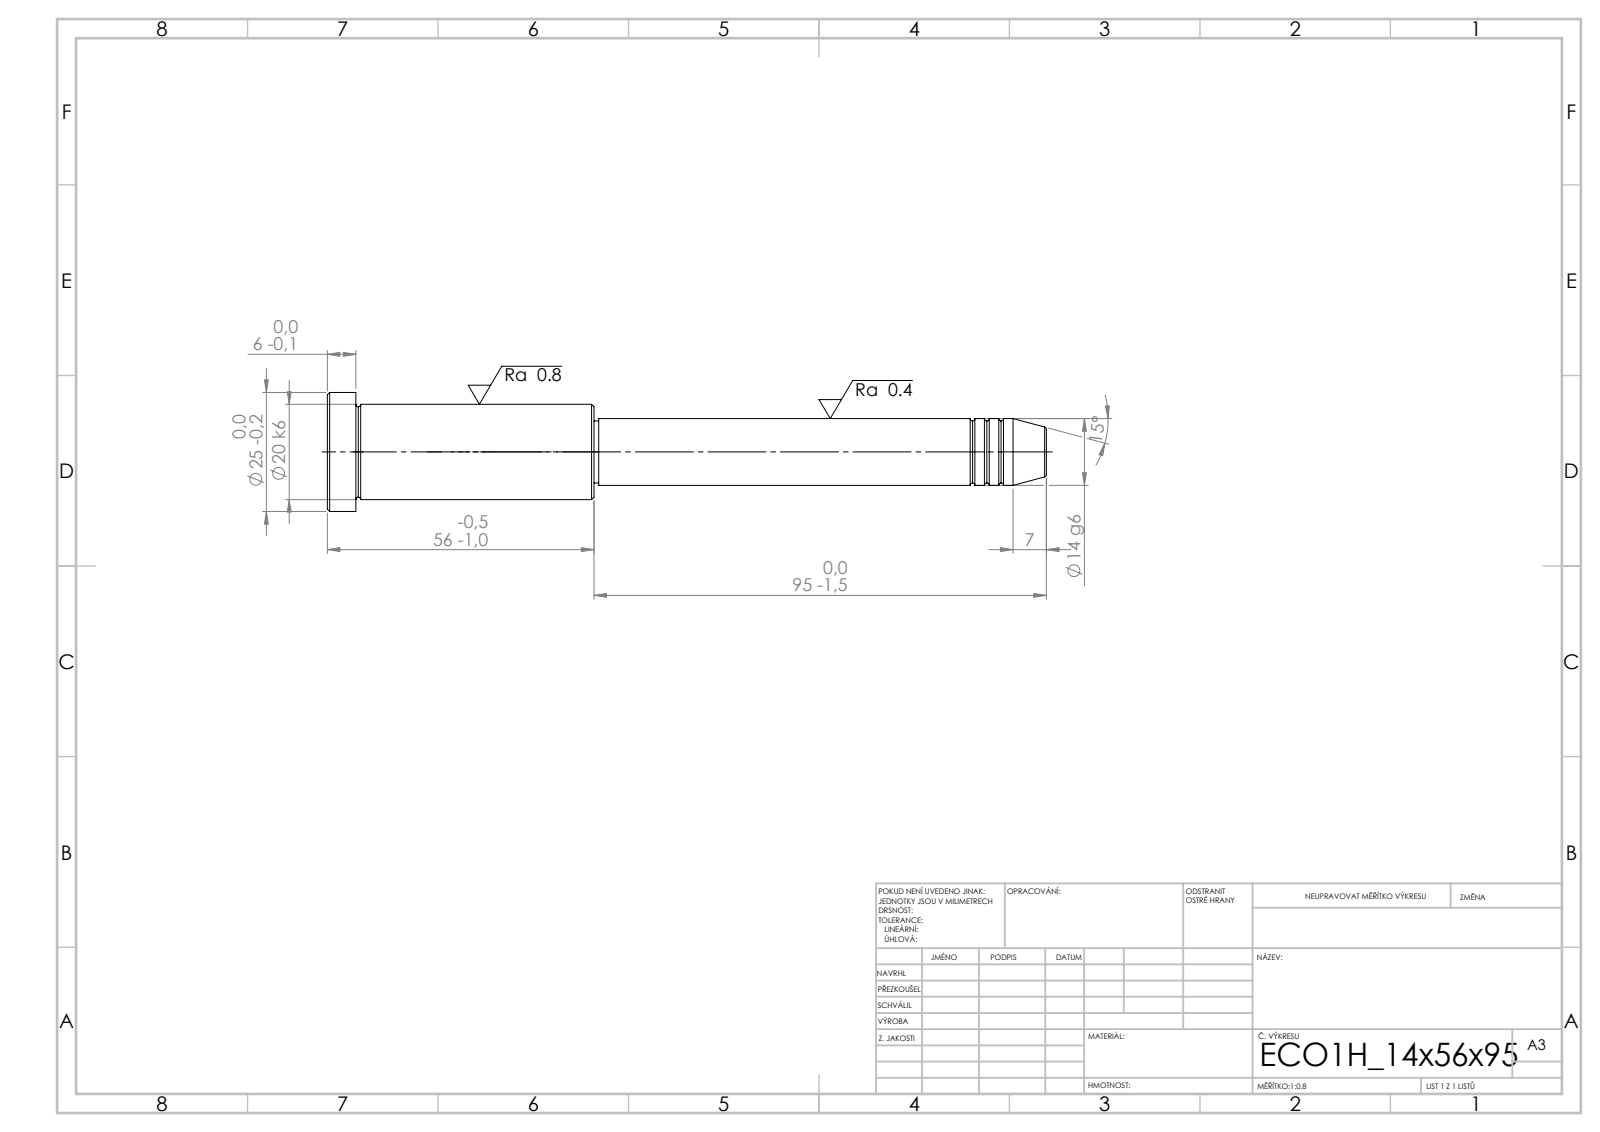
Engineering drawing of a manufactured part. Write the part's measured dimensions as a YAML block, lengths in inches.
step_written_by: "SolidWorks 2019 (CONFIG_CONTROL_DESIGN)"
units: inches
bodies: {solids: 1, faces: 43, planar: 5, cylindrical: 14, other: 24}
overall_size: [5.945, 0.984, 0.984]
volume: 2.008
surface_area: 13.58
round_bosses_or_shafts:
  - {diameter: 0.984, count: 1}
  - {diameter: 0.787, count: 1}
  - {diameter: 0.551, count: 1}
  - {diameter: 0.512, count: 1}
face_to_face_distances: [0.236, 1.969, 2.205, 3.74, 5.709, 5.945, 3.701, 0.039, 2.008, 2.244]
